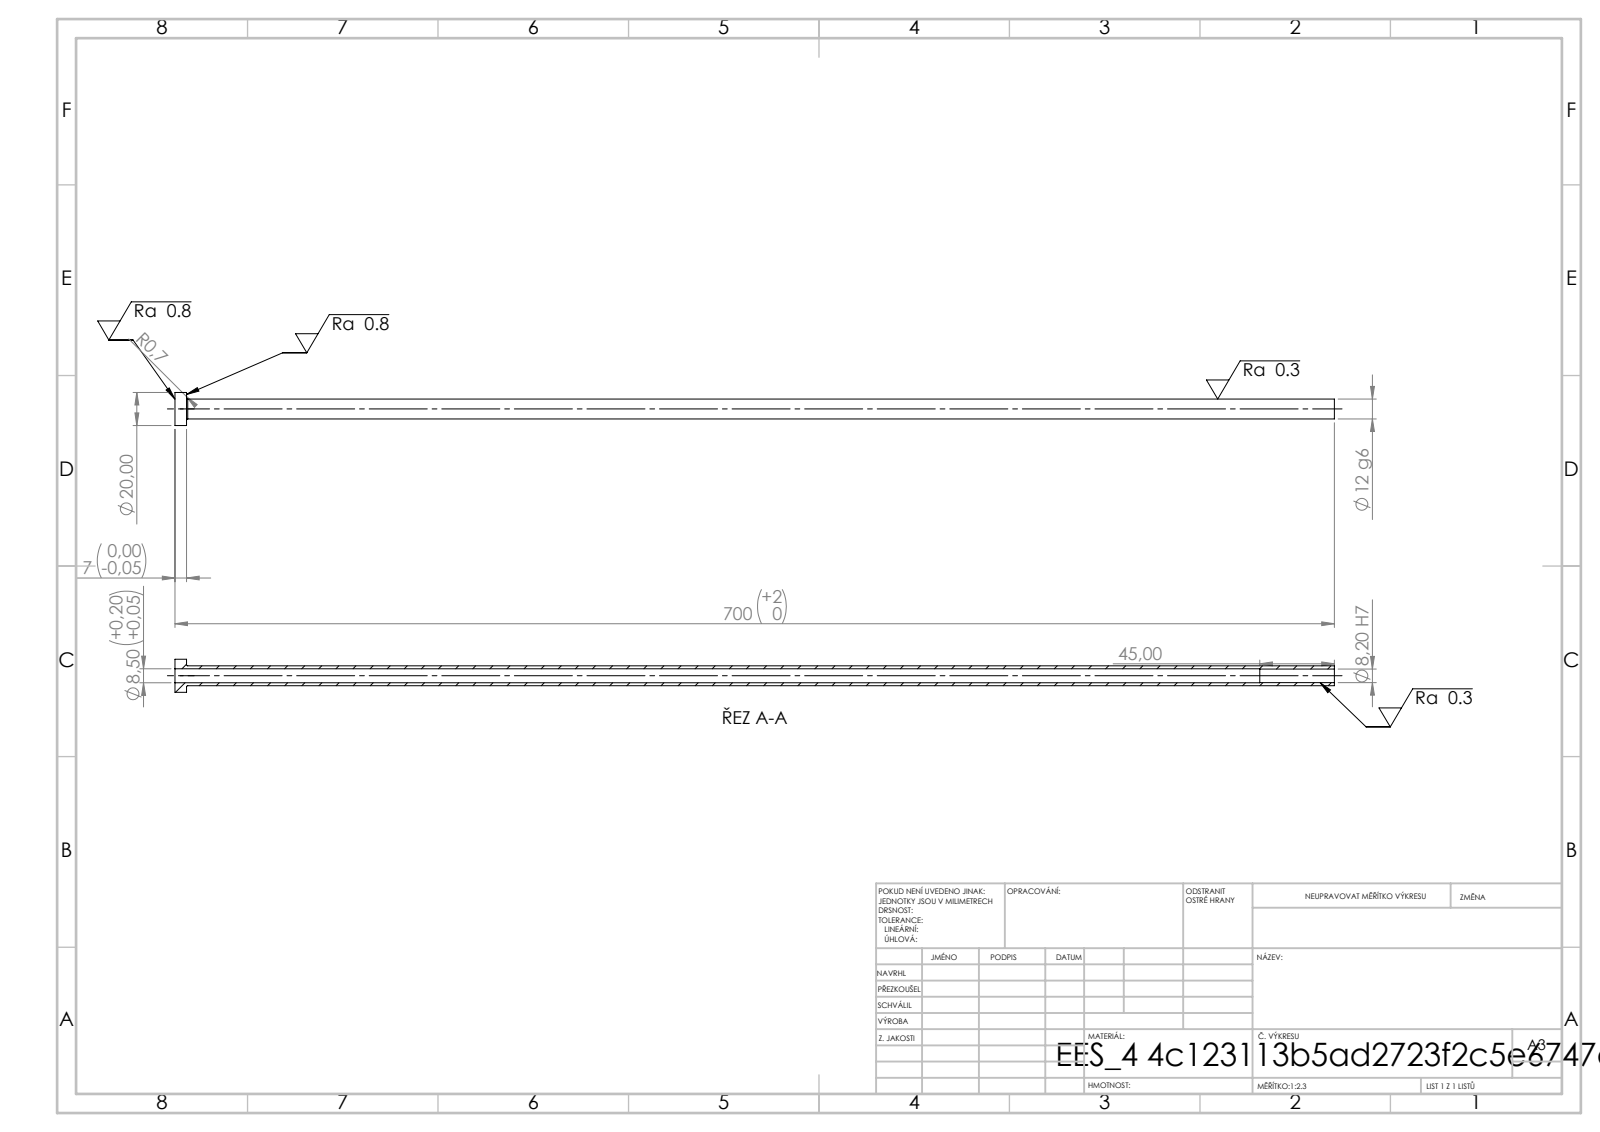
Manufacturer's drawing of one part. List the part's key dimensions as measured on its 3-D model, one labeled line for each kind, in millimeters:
STEP written by: SolidWorks 2019 (CONFIG_CONTROL_DESIGN)
Units: millimetres
Bodies: 1 solid, 14 faces (4 planar, 8 cylindrical, 2 other)
Overall size (bounding box): 700 × 20 × 20
Volume: 41 035 mm³ · Surface area: 45 727 mm²
Round holes (diameter × count): ⌀8.2 ×1, ⌀8.5 ×1
Round bosses / shafts (diameter × count): ⌀20 ×1, ⌀12 ×1
Main face-to-face distances: 7, 700, 693, 655, 648, 45
